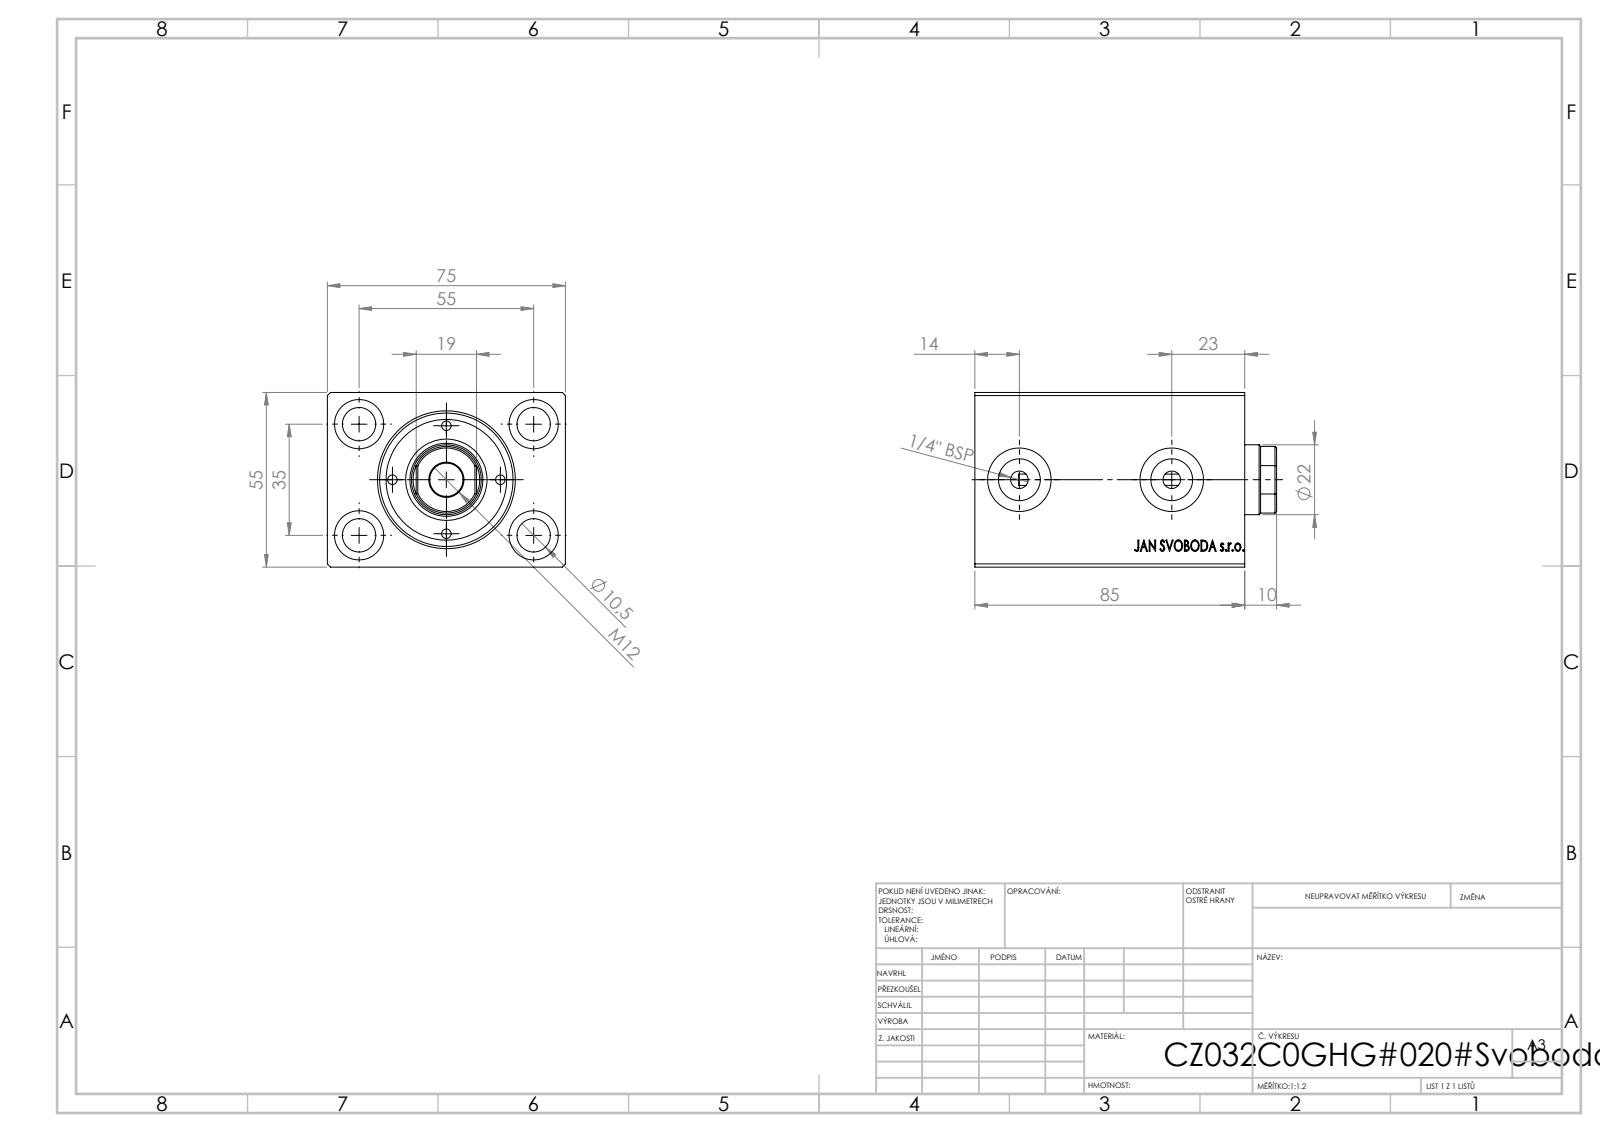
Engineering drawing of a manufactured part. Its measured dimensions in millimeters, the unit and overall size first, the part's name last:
Units: millimetres
Overall size (bounding box): 85 × 75 × 55
Round holes (diameter × count): ⌀10.5 ×4, ⌀15.5 ×4, ⌀5.5 ×2, ⌀8 ×2, ⌀13.16 ×2, ⌀20 ×2, ⌀32 ×1, ⌀36 ×1, ⌀42 ×1
Main face-to-face distances: 55, 75, 85, 13.6, 84.8, 10.33, 74.67, 71.2, 13.8, 74.8
Hole centre spacings: 32.6, 35, 55, 65.19, 28, 48
Volume: 245 088 mm³ · Surface area: 50 923 mm²
Bodies: 1 solid, 826 faces (398 planar, 46 cylindrical, 382 other)
STEP written by: SolidWorks 2019 (CONFIG_CONTROL_DESIGN)
